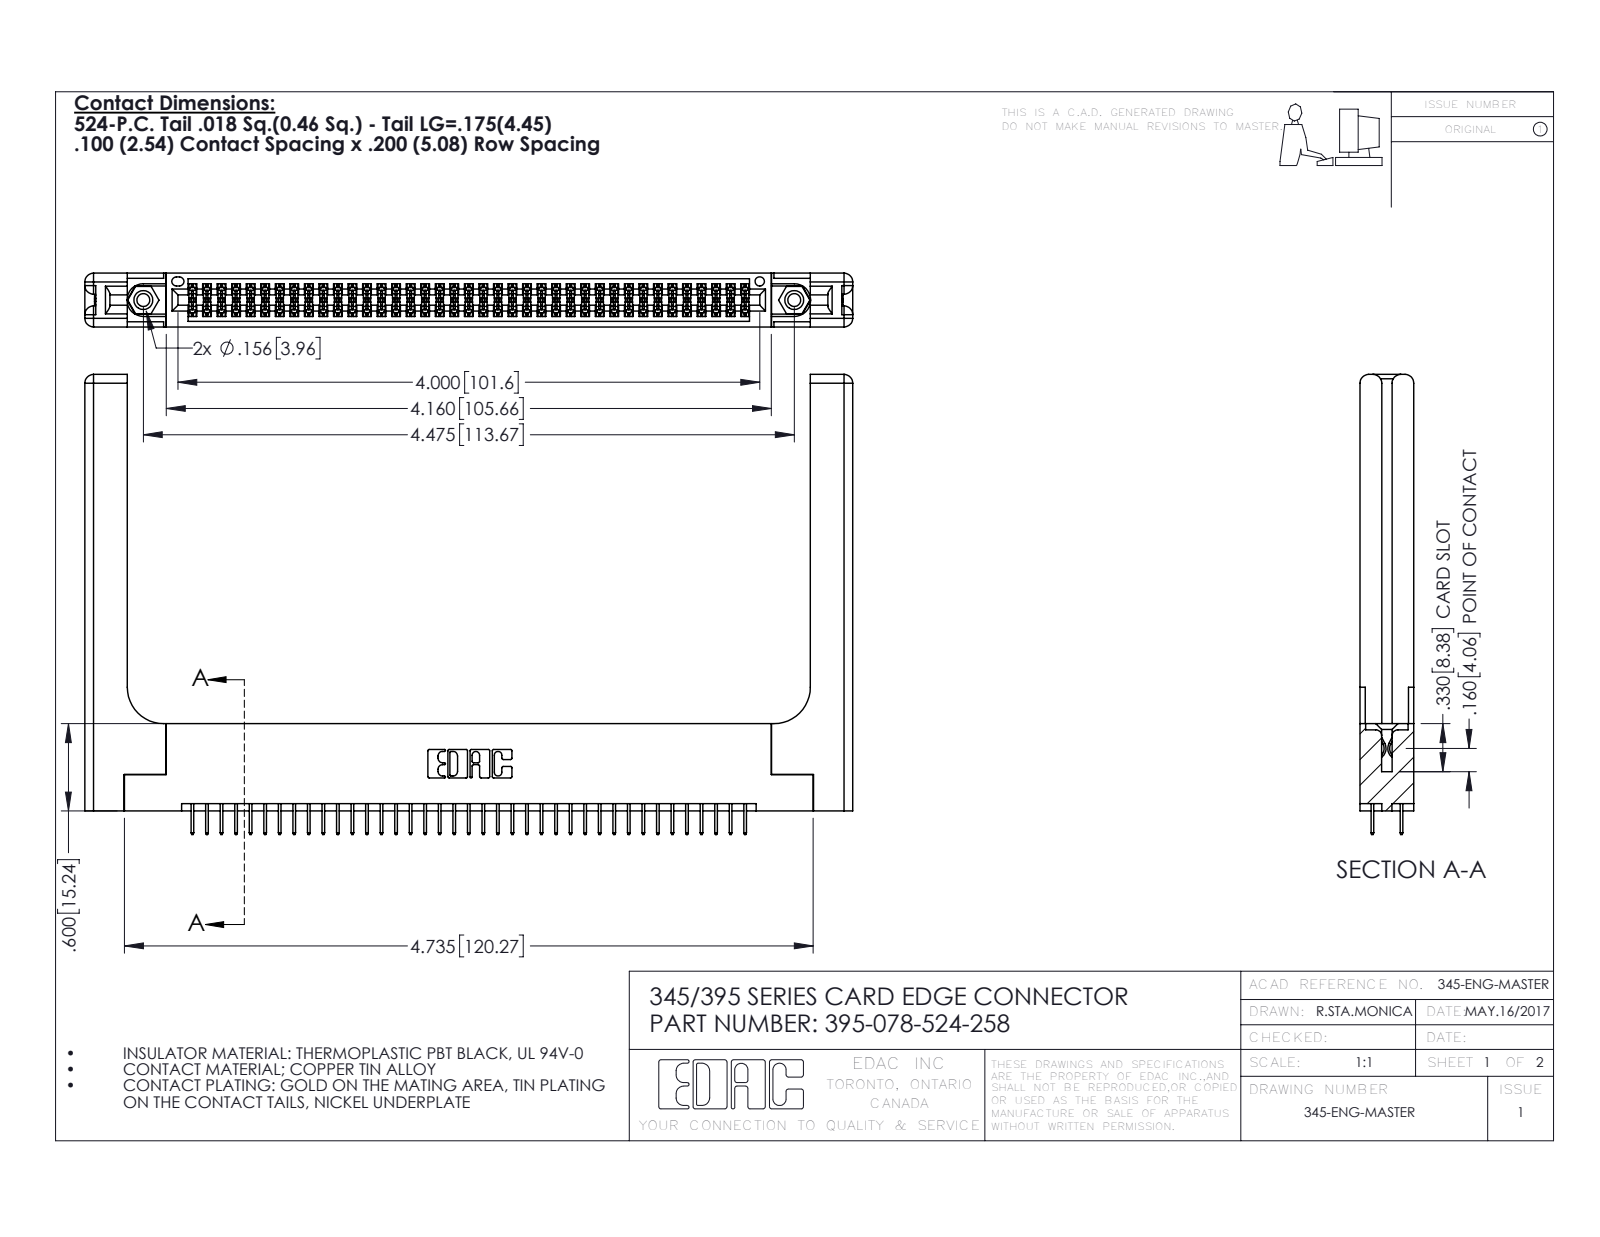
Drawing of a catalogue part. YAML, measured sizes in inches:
part_name: "345 Part_Flush Mounting Lugs - 0.156 Dia-TH; 345-220-058_345-220-058; 345-250-001_345-250-001-102; 395-078-524-258 (+1 more)"
step_written_by: "SolidWorks 2016 (CONFIG_CONTROL_DESIGN)"
units: inches
bodies: {solids: 83, faces: 4594, planar: 3270, cylindrical: 1264, other: 60}
overall_size: [5.279, 3.162, 0.37]
volume: 1.303
surface_area: 36.78
round_holes:
  - {diameter: 0.089, count: 2}
  - {diameter: 0.125, count: 2}
  - {diameter: 0.156, count: 2}
  - {diameter: 0.064, count: 1}
round_bosses_or_shafts:
  - {diameter: 0.155, count: 2}
partial_cylinders:
  - {radius: 0.006, count: 117}
  - {radius: 0.01, count: 22}
  - {radius: 0.06, count: 16}
  - {radius: 0.007, count: 6}
  - {radius: 0.031, count: 6}
  - {radius: 0.026, count: 3}
  - {radius: 0.014, count: 2}
  - {radius: 0.019, count: 2}
face_to_face_distances: [0.37, 0.072, 0.298, 0.2, 0.098, 0.272, 0.025, 0.225, 0.148, 0.15]
hole_center_spacings: [0.27, 4.239, 4.475]
